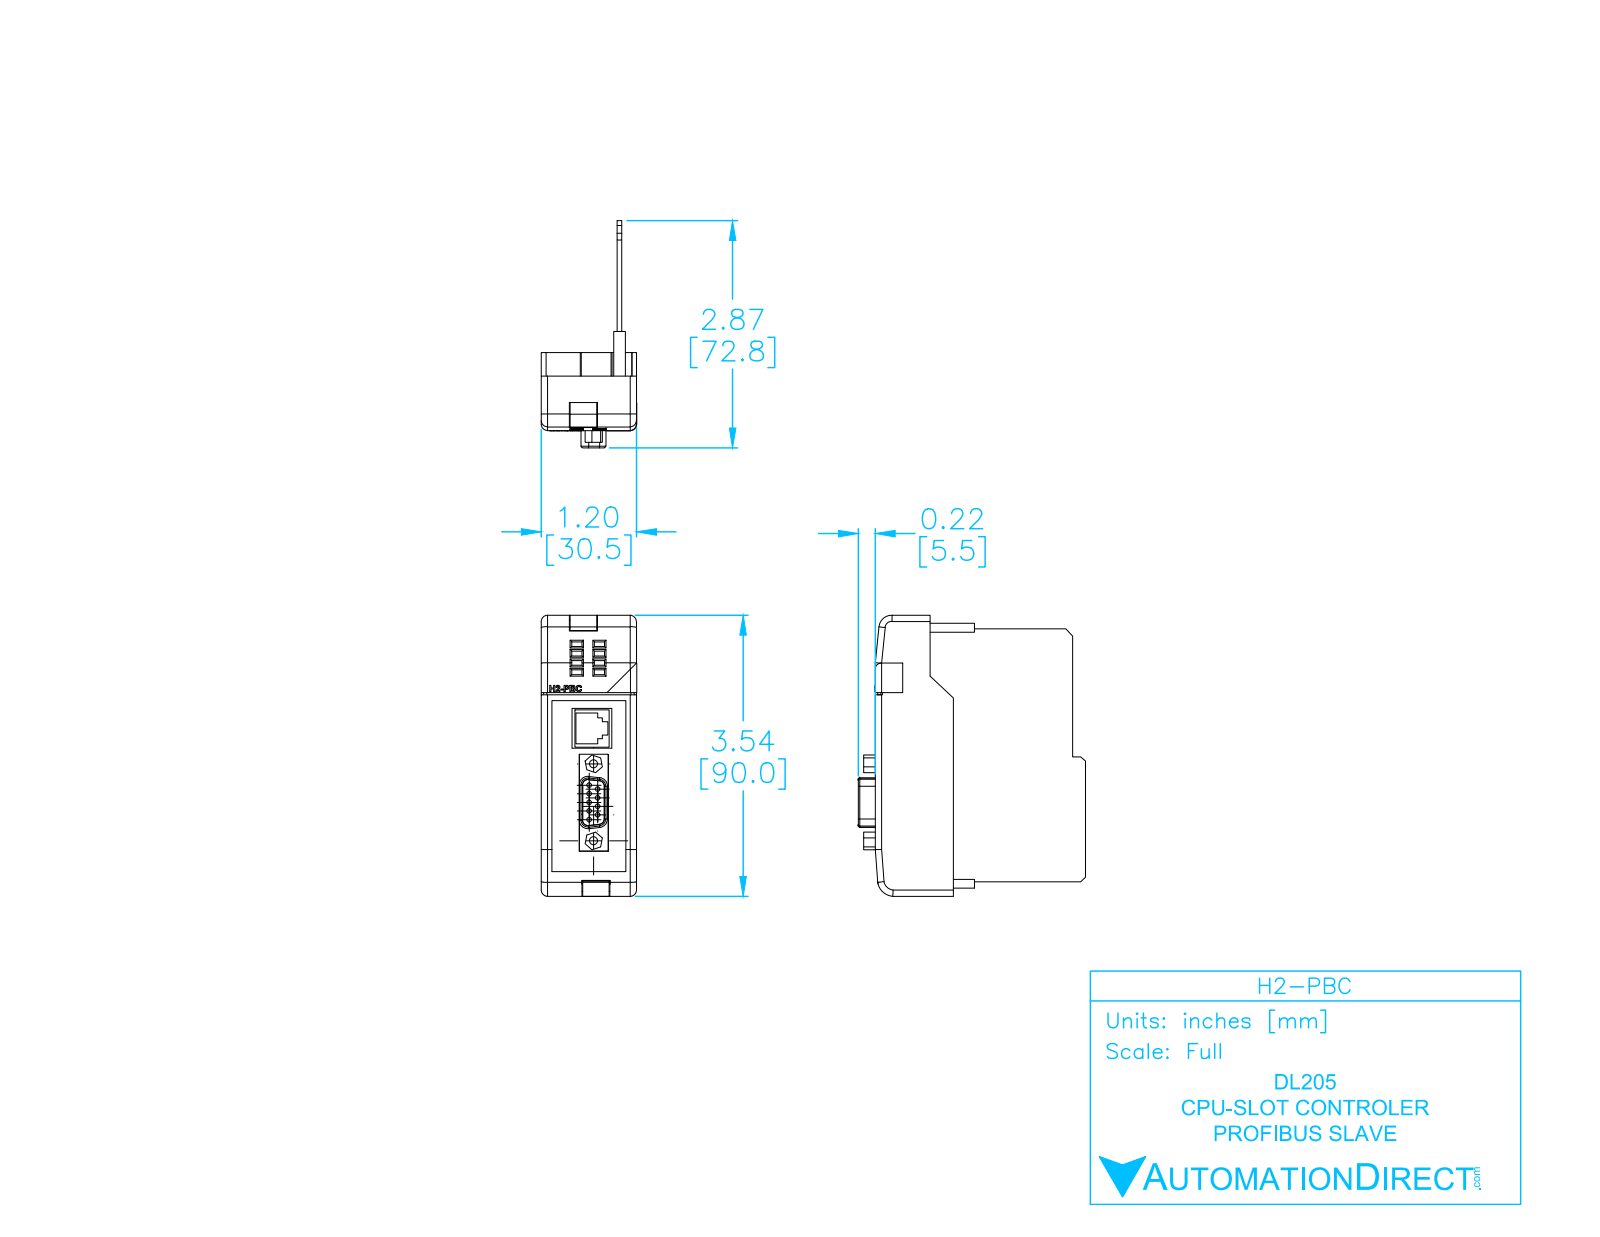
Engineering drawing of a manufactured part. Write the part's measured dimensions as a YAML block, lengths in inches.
part_name: "H2-PBC"
step_written_by: "SolidWorks 2009 (AUTOMOTIVE_DESIGN)"
units: inches
bodies: {solids: 7, faces: 461, planar: 281, cylindrical: 126, other: 54}
overall_size: [3.543, 2.865, 1.203]
volume: 1.143
surface_area: 46.27
round_holes:
  - {diameter: 0.059, count: 9}
  - {diameter: 0.098, count: 2}
partial_cylinders:
  - {radius: 0.02, count: 36}
  - {radius: 0.079, count: 11}
  - {radius: 0.069, count: 8}
  - {radius: 0.01, count: 4}
  - {radius: 0.089, count: 4}
  - {radius: 0.039, count: 2}
  - {radius: 0.103, count: 1}
  - {radius: 0.149, count: 1}
face_to_face_distances: [0.059, 0.186, 0.02, 0.127, 0.245, 0.956, 1.142, 0.039, 1.201, 1.015]
hole_center_spacings: [0.108, 0.217, 0.119, 0.122, 0.191, 0.198, 0.325, 0.287]
